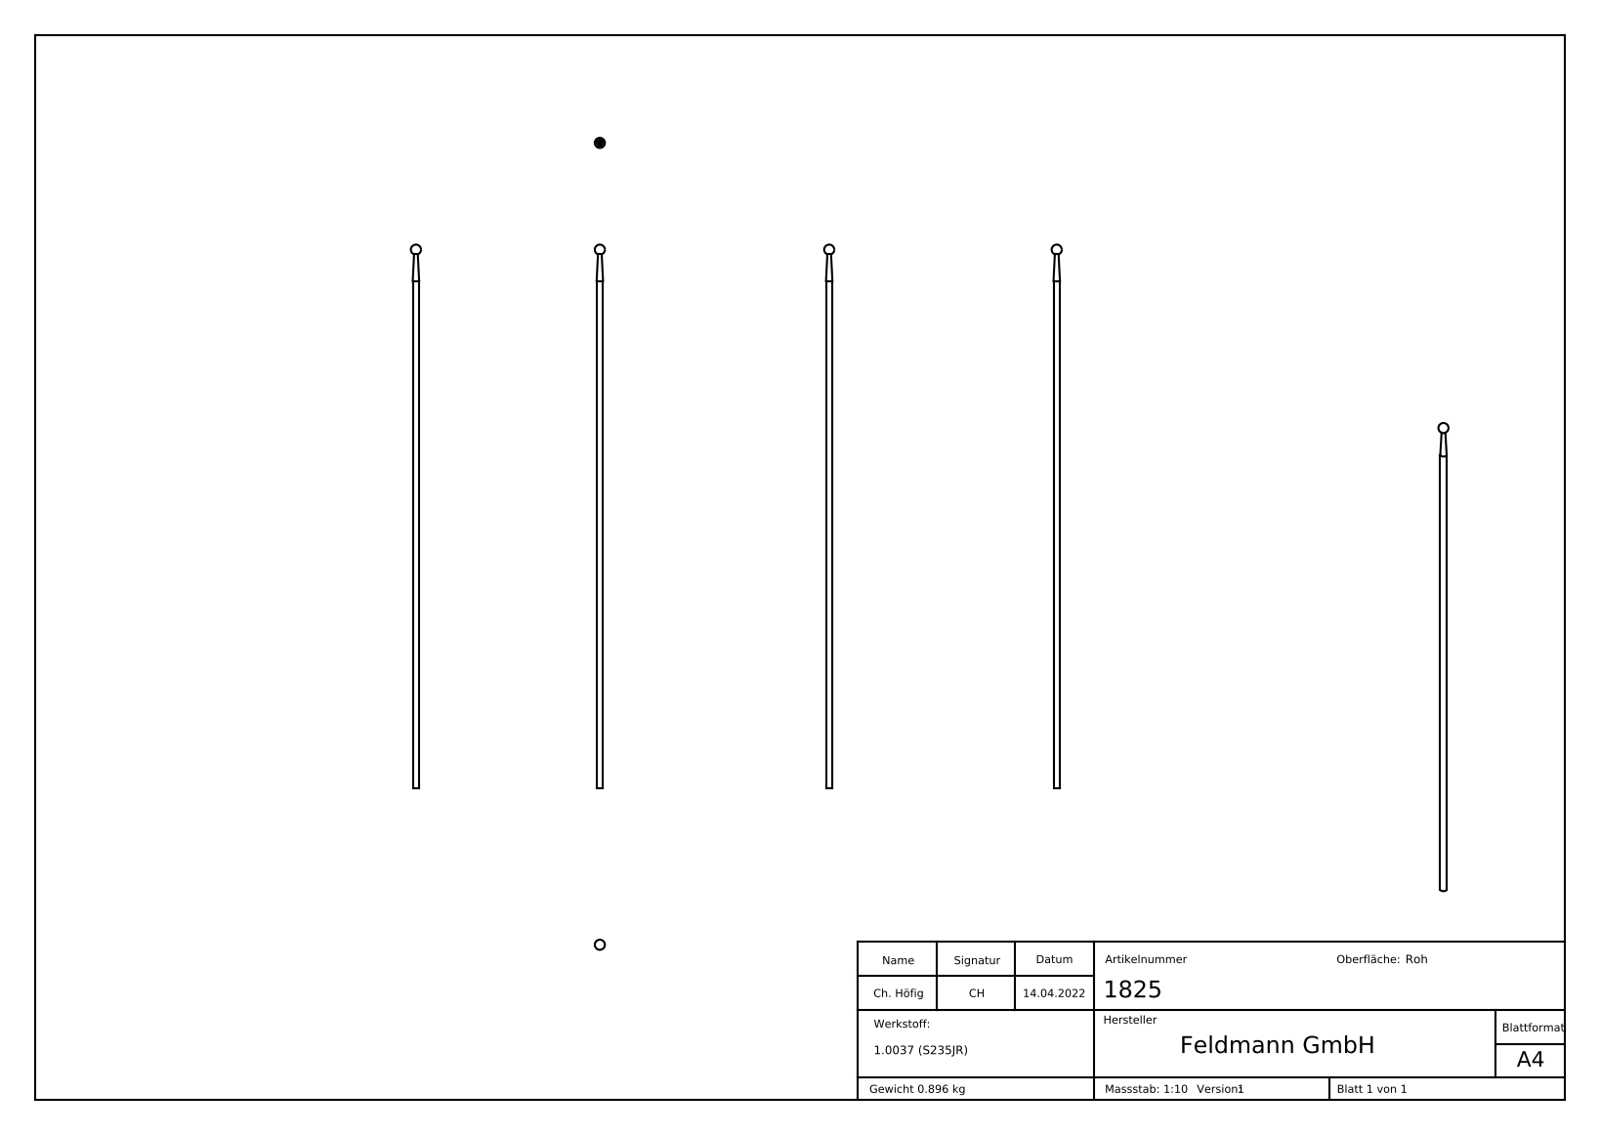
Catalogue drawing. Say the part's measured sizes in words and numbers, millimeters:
The part is named "1825". Its 3-D file was written by "SolidWorks 2018 (CONFIG_CONTROL_DESIGN)". It is 1 solid with 215 faces: 113 planar, 1 cylindrical and 101 other. Overall it measures 1020 by 19 by 19 millimeters. Its volume is 114 835 cubic millimeters and its surface area 38 585 square millimeters. Round bosses or shafts: 1 of diameter 12. The main face-to-face distances are 1.76, 2.32, 1.96, 2.31, 0.49, 0.47, 1.62, 0.41, 1.78, 1.21.
